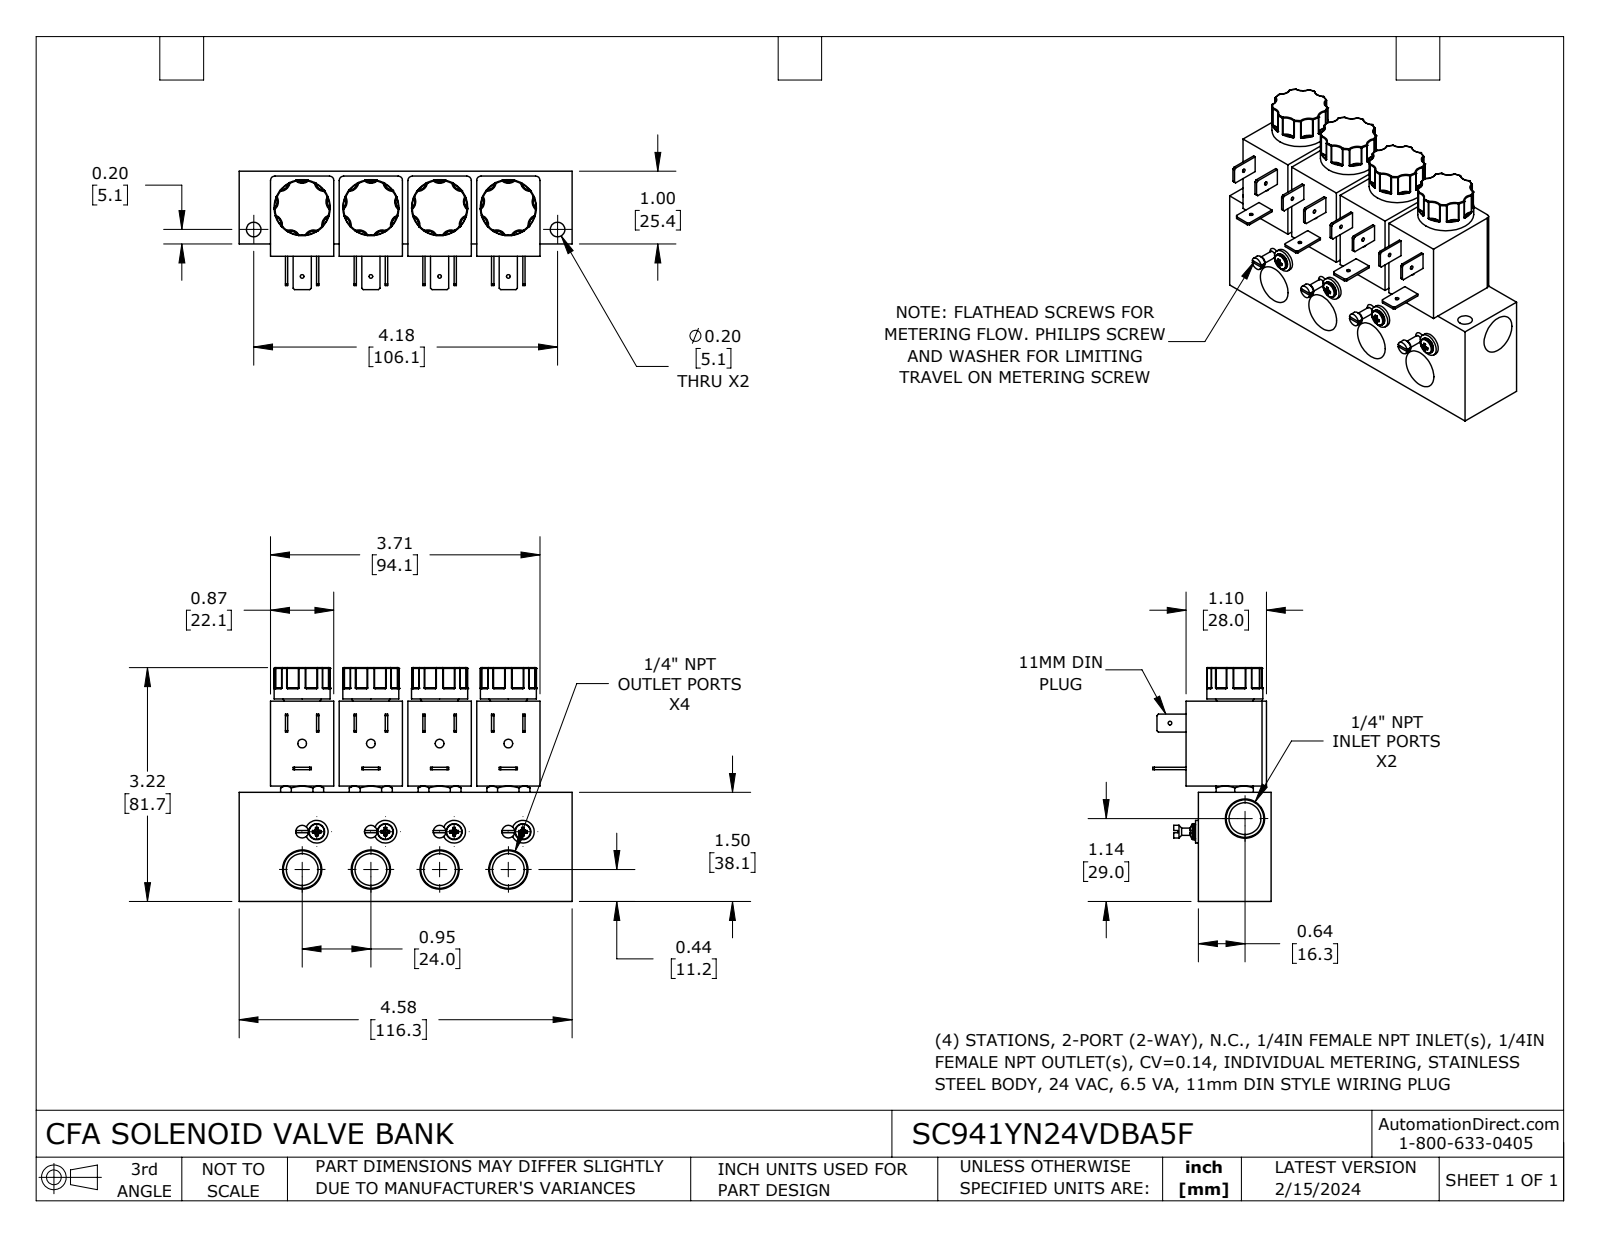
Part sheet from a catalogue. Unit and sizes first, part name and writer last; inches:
Units: inches
Overall size (bounding box): 4.578 × 3.215 × 1.627
Round holes (diameter × count): ⌀0.05 ×5, ⌀0.438 ×5, ⌀0.12 ×4, ⌀0.2 ×2
Round bosses / shafts (diameter × count): ⌀0.77 ×4, ⌀0.312 ×4, ⌀0.219 ×4, ⌀0.175 ×4, ⌀0.1 ×4
Partial cylindrical surfaces — rounded edges, fillets, slot ends (radius × count): R0.01 ×72, R0.133 ×28, R0.06 ×8, R0.132 ×8
Main face-to-face distances: 1, 0.945, 1.169, 0.169, 1.89, 0.87, 1.815, 1.5, 0.065, 0.935
Hole centre spacings: 0.945, 1.732, 1.973, 0.945, 1.89, 1.89, 2.835, 1.973
Volume: 11.49 in³ · Surface area: 68.21 in²
Bodies: 1 solid, 1098 faces (284 planar, 260 cylindrical, 554 other)
Part name (STEP PRODUCT): SC941YN24VDBA5F
STEP written by: SolidWorks 2023 (CONFIG_CONTROL_DESIGN)
